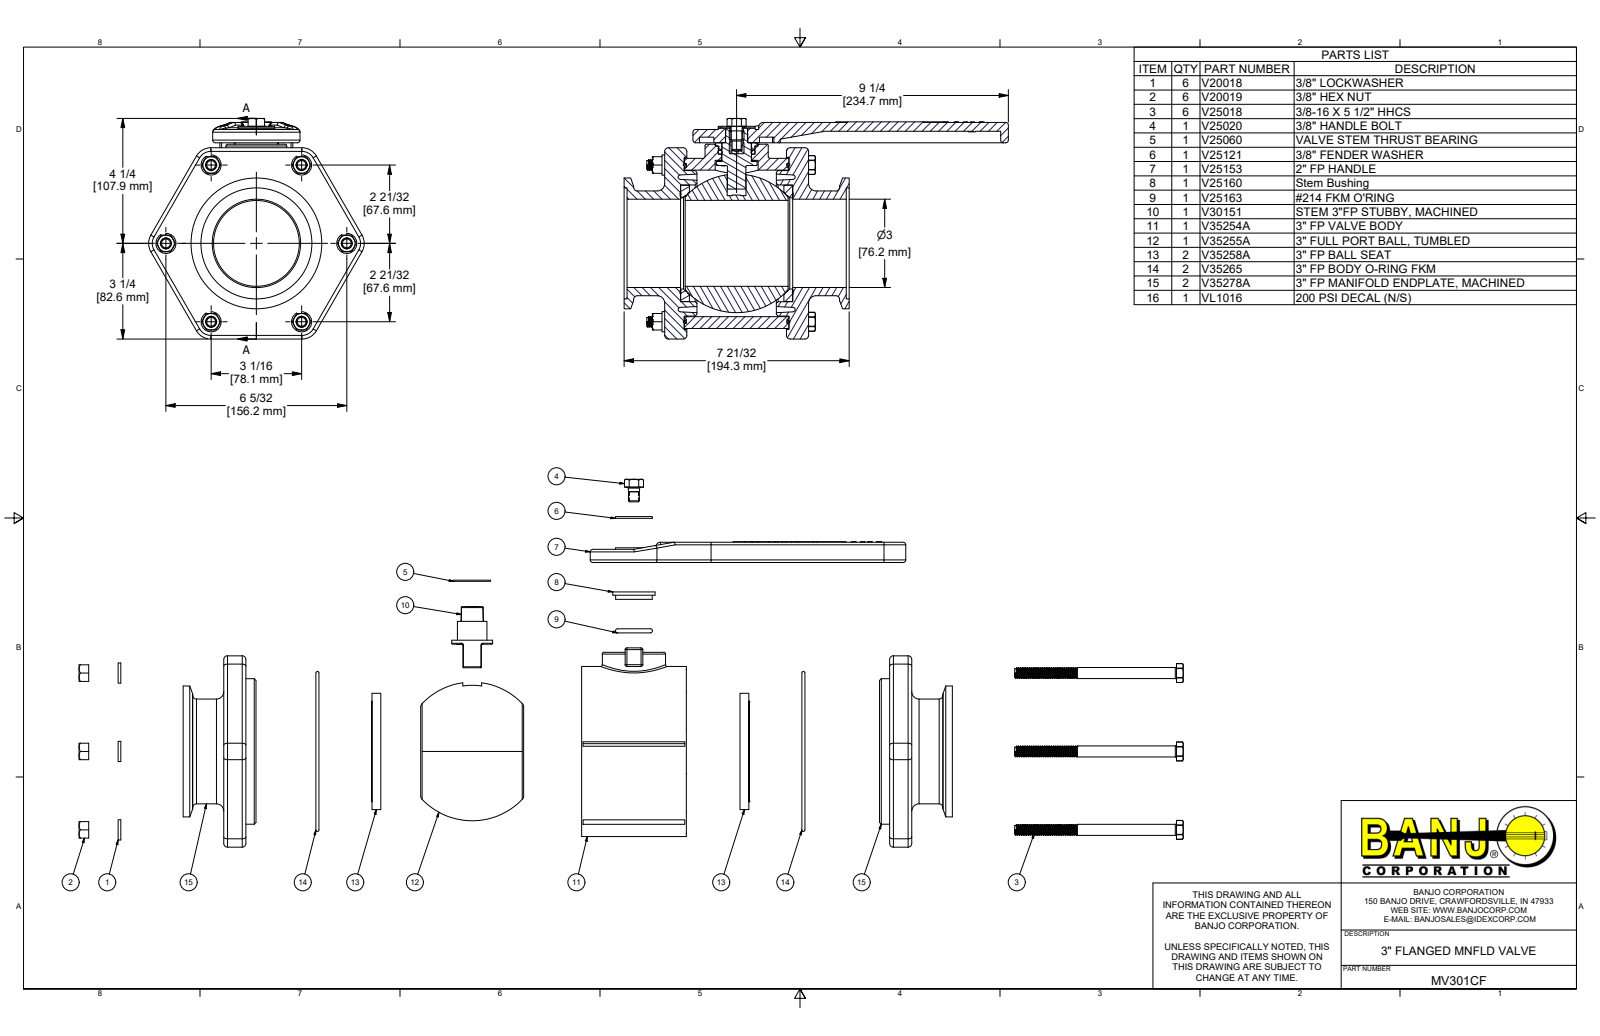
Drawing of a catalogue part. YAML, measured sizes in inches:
part_name: "MV301CF; V35254A; V35278A; V35278AX (+8 more)"
step_written_by: "Autodesk Inventor 2019 (AUTOMOTIVE_DESIGN)"
units: inches
bodies: {solids: 34, faces: 2002, planar: 666, cylindrical: 906, other: 430}
overall_size: [13.065, 7.497, 7.331]
volume: 118.6
surface_area: 732
round_holes:
  - {diameter: 0.171, count: 12}
  - {diameter: 0.375, count: 7}
  - {diameter: 0.307, count: 6}
  - {diameter: 0.385, count: 6}
  - {diameter: 0.44, count: 6}
  - {diameter: 0.307, count: 1}
  - {diameter: 0.406, count: 1}
  - {diameter: 0.681, count: 1}
  - {diameter: 0.962, count: 1}
  - {diameter: 1, count: 1}
  - {diameter: 1.016, count: 1}
  - {diameter: 1.245, count: 1}
round_bosses_or_shafts:
  - {diameter: 0.687, count: 6}
  - {diameter: 0.361, count: 6}
  - {diameter: 0.3, count: 6}
  - {diameter: 5.78, count: 1}
  - {diameter: 5.138, count: 1}
  - {diameter: 4.944, count: 1}
  - {diameter: 4.445, count: 1}
  - {diameter: 3.95, count: 1}
partial_cylinders:
  - {radius: 0.125, count: 24}
  - {radius: 0.06, count: 12}
  - {radius: 0.032, count: 10}
  - {radius: 0.09, count: 8}
  - {radius: 0.32, count: 6}
  - {radius: 0.562, count: 6}
  - {radius: 0.059, count: 2}
  - {radius: 0.084, count: 2}
face_to_face_distances: [0.665, 4.225, 4.89, 0.538, 4.352, 0.127, 3.687, 0.75, 0.085, 4.14]
hole_center_spacings: [2.805, 2.264, 5.418, 5.433, 0.813, 1.452, 2.804, 3.586]
